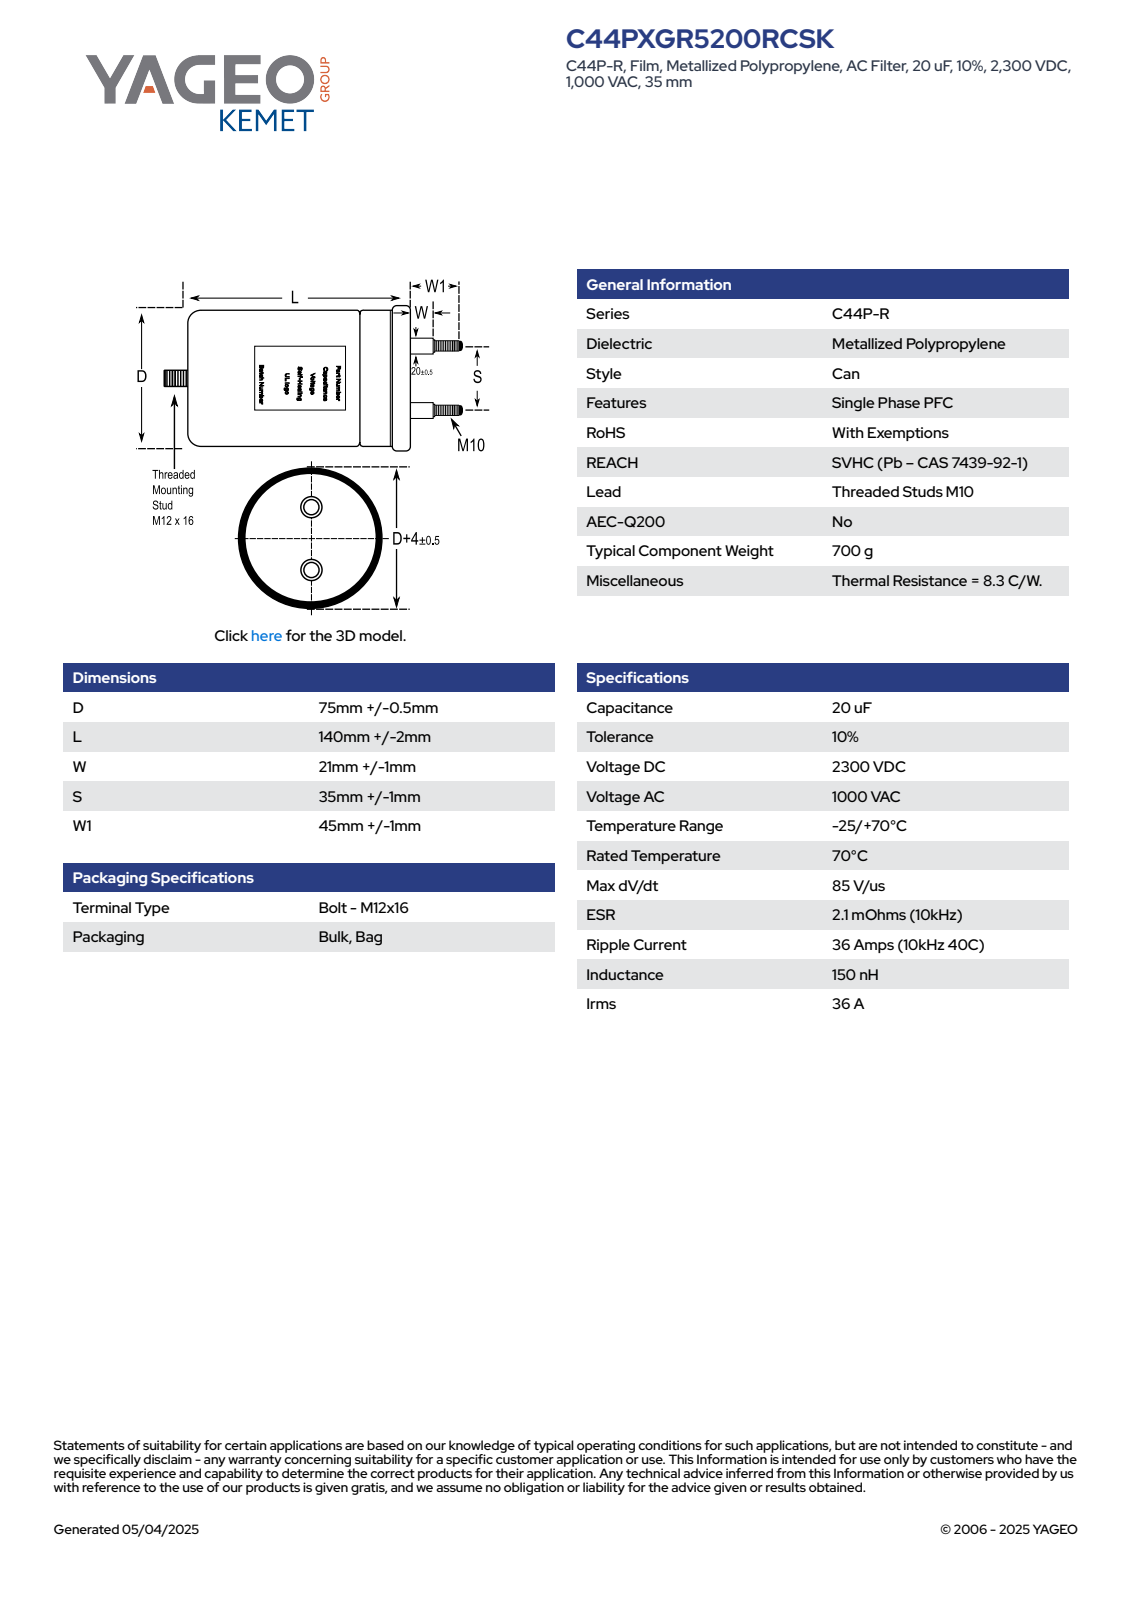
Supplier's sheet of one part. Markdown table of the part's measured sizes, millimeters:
| quantity | value |
| --- | --- |
| part name | CFP_C44P_75X140_D75.5L142S35 |
| STEP written by | SolidWorks 2014 (AUTOMOTIVE_DESIGN) |
| units | millimeters |
| bodies | 1 solid, 105 faces (32 planar, 36 cylindrical, 37 other) |
| overall size | 204 × 80 × 80 |
| volume | 656 563 mm³ |
| surface area | 47 956 mm² |
| round bosses / shafts (diameter × count) | 12 × 3, 20.5 × 2, 10 × 2, 80 × 1, 75.5 × 1 |
| partial cylindrical surfaces (radius × count) | 37.76 × 1 |
| main face-to-face distances | 142, 163, 21, 137.44, 4.56, 25.56, 188, 50.56, 46, 25 |
